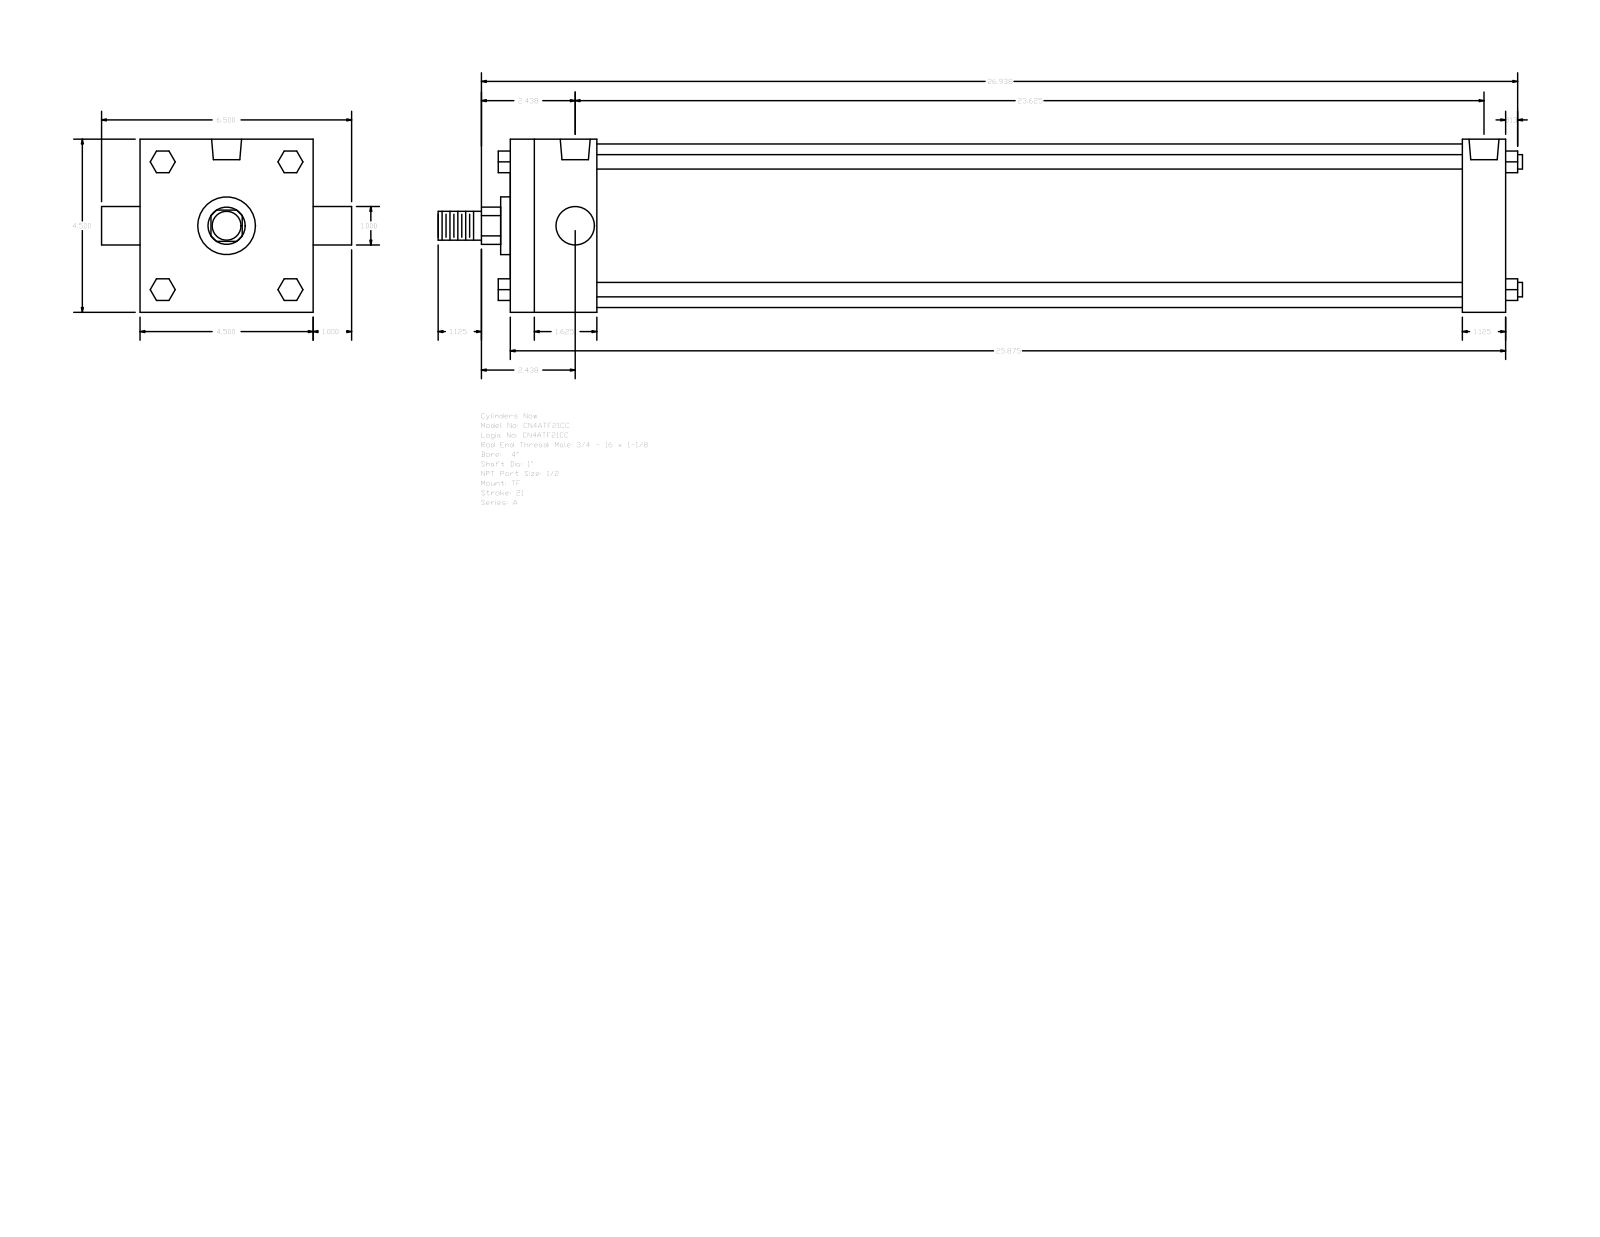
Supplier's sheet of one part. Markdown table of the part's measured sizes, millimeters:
| quantity | value |
| --- | --- |
| part name | A_TF__0400_1 |
| STEP written by | GSSL Pune (CONFIG_CONTROL_DESIGN) |
| units | millimeters |
| bodies | 0 solids, 120 faces (92 planar, 28 cylindrical, 0 other) |
| overall size | 715.96 × 165.1 × 114.3 |
| round holes (diameter × count) | 8.73 × 3, 19.77 × 2 |
| round bosses / shafts (diameter × count) | 9.53 × 4, 25.4 × 2, 107.95 × 1, 38.1 × 1, 19.05 × 1 |
| partial cylindrical surfaces (radius × count) | 12.29 × 1 |
| main face-to-face distances | 114.3, 657.22, 28.57, 628.65, 57.15, 571.5, 600.07, 14.29, 42.16, 73.03 |
| hole center spacings | 3.18, 596.9, 593.72, 600.08 |
